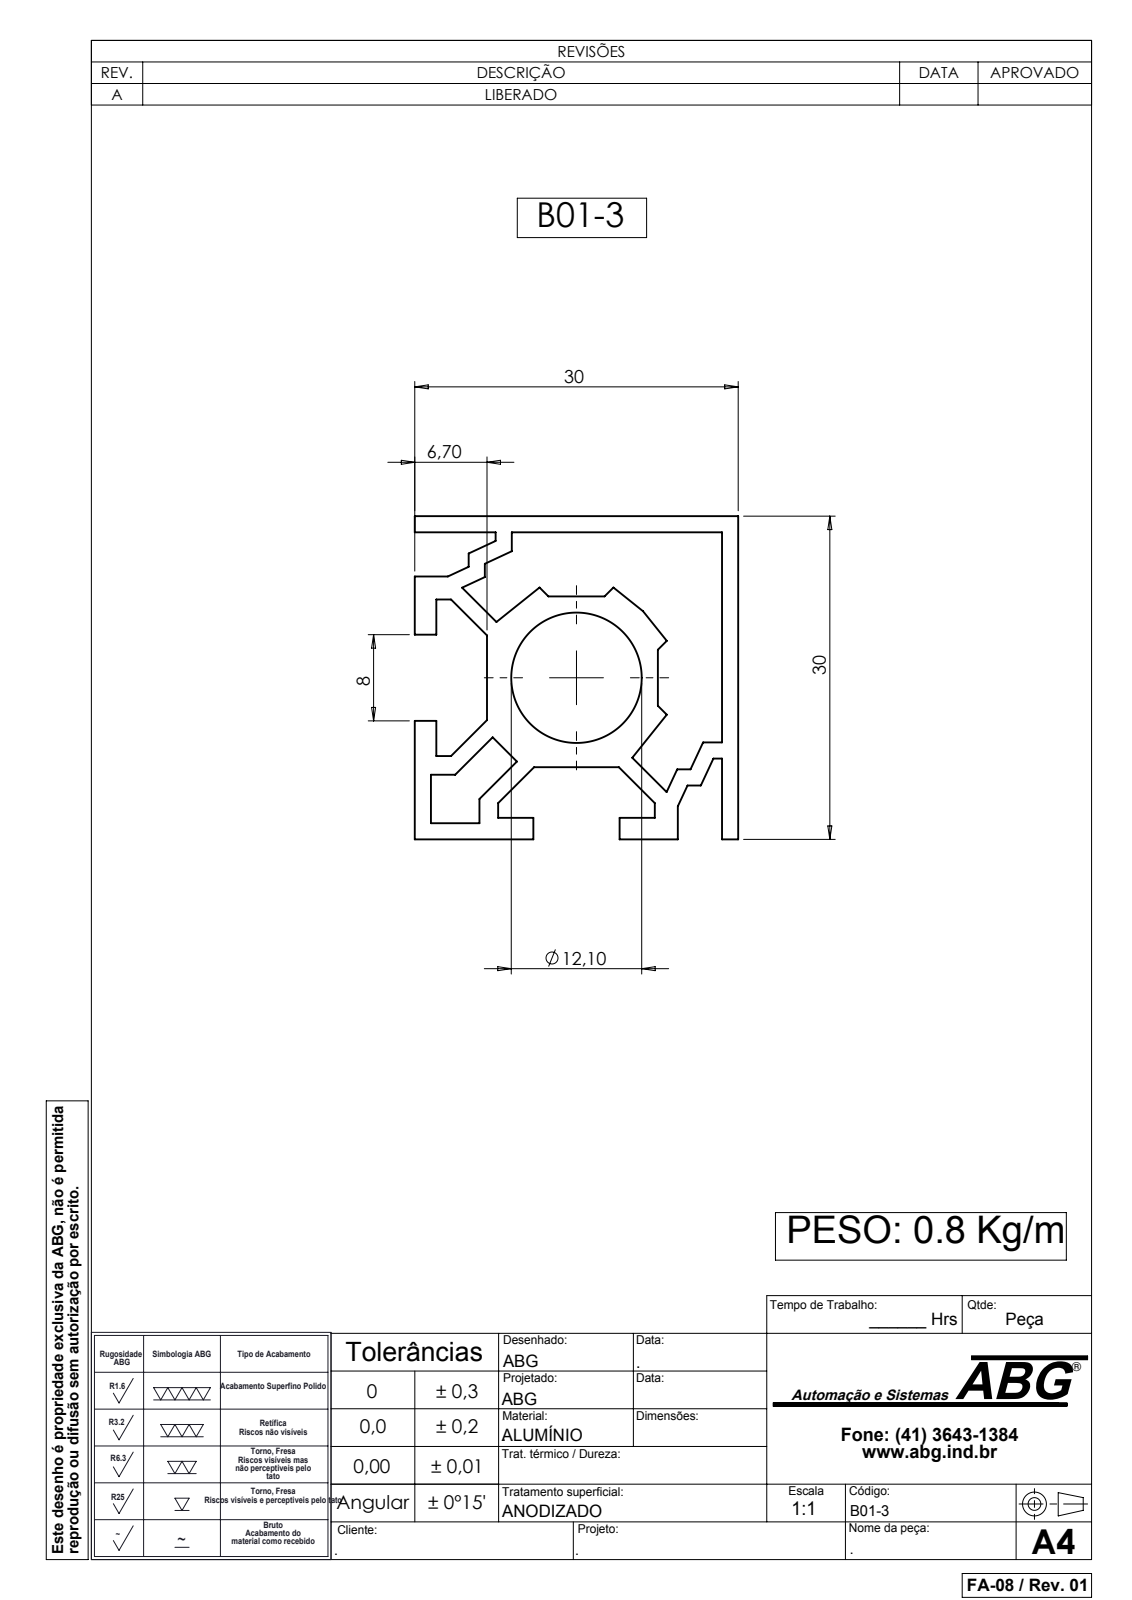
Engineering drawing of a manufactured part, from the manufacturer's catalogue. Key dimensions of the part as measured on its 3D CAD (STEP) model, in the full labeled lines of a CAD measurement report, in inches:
Part name (STEP PRODUCT): B01-3
STEP written by: SolidWorks 2007 (CONFIG_CONTROL_DESIGN)
Units: inches
Bodies: 1 solid, 71 faces (69 planar, 2 cylindrical, 0 other)
Overall size (bounding box): 236.22 × 1.181 × 1.181
Volume: 119.2 in³ · Surface area: 3 283 in²
Round holes (diameter × count): ⌀0.476 ×1
Main face-to-face distances: 0.059, 1.122, 1.181, 0.079, 0.264, 0.858, 0.917, 0.185, 1.043, 1.102
